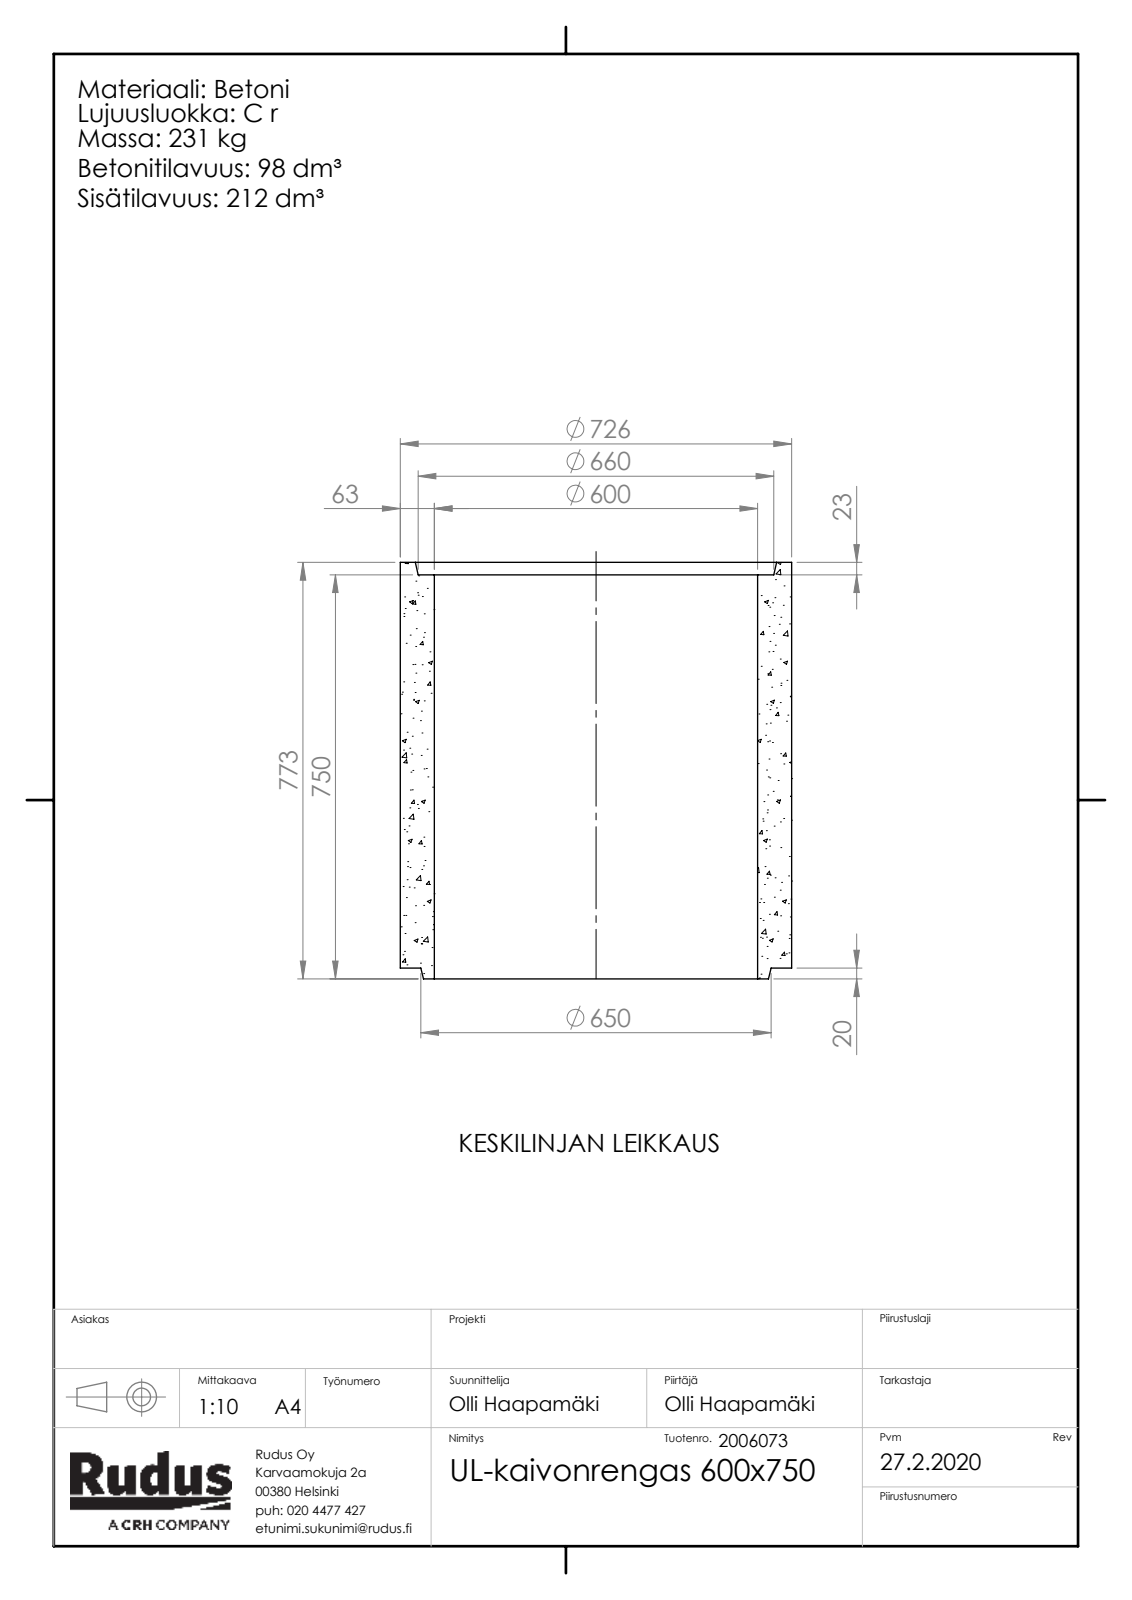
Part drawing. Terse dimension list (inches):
name: EK-osa-kaivorunko_UL-kaivonrengas; Rudus 2006073 UL-kaivonrengas 600x750
written by: SolidWorks 2019 (CONFIG_CONTROL_DESIGN)
unit: in
bodies: 1 solid, 89 faces (7 planar, 0 cylindrical, 82 other)
size: 30.433 × 28.583 × 28.583
volume: 5 992 in³; area: 5 377 in²
face distances: 29.646, 28.74, 0.906, 0.787, 29.528, 30.433, 15.217, 14.429, 14.311, 17.518
